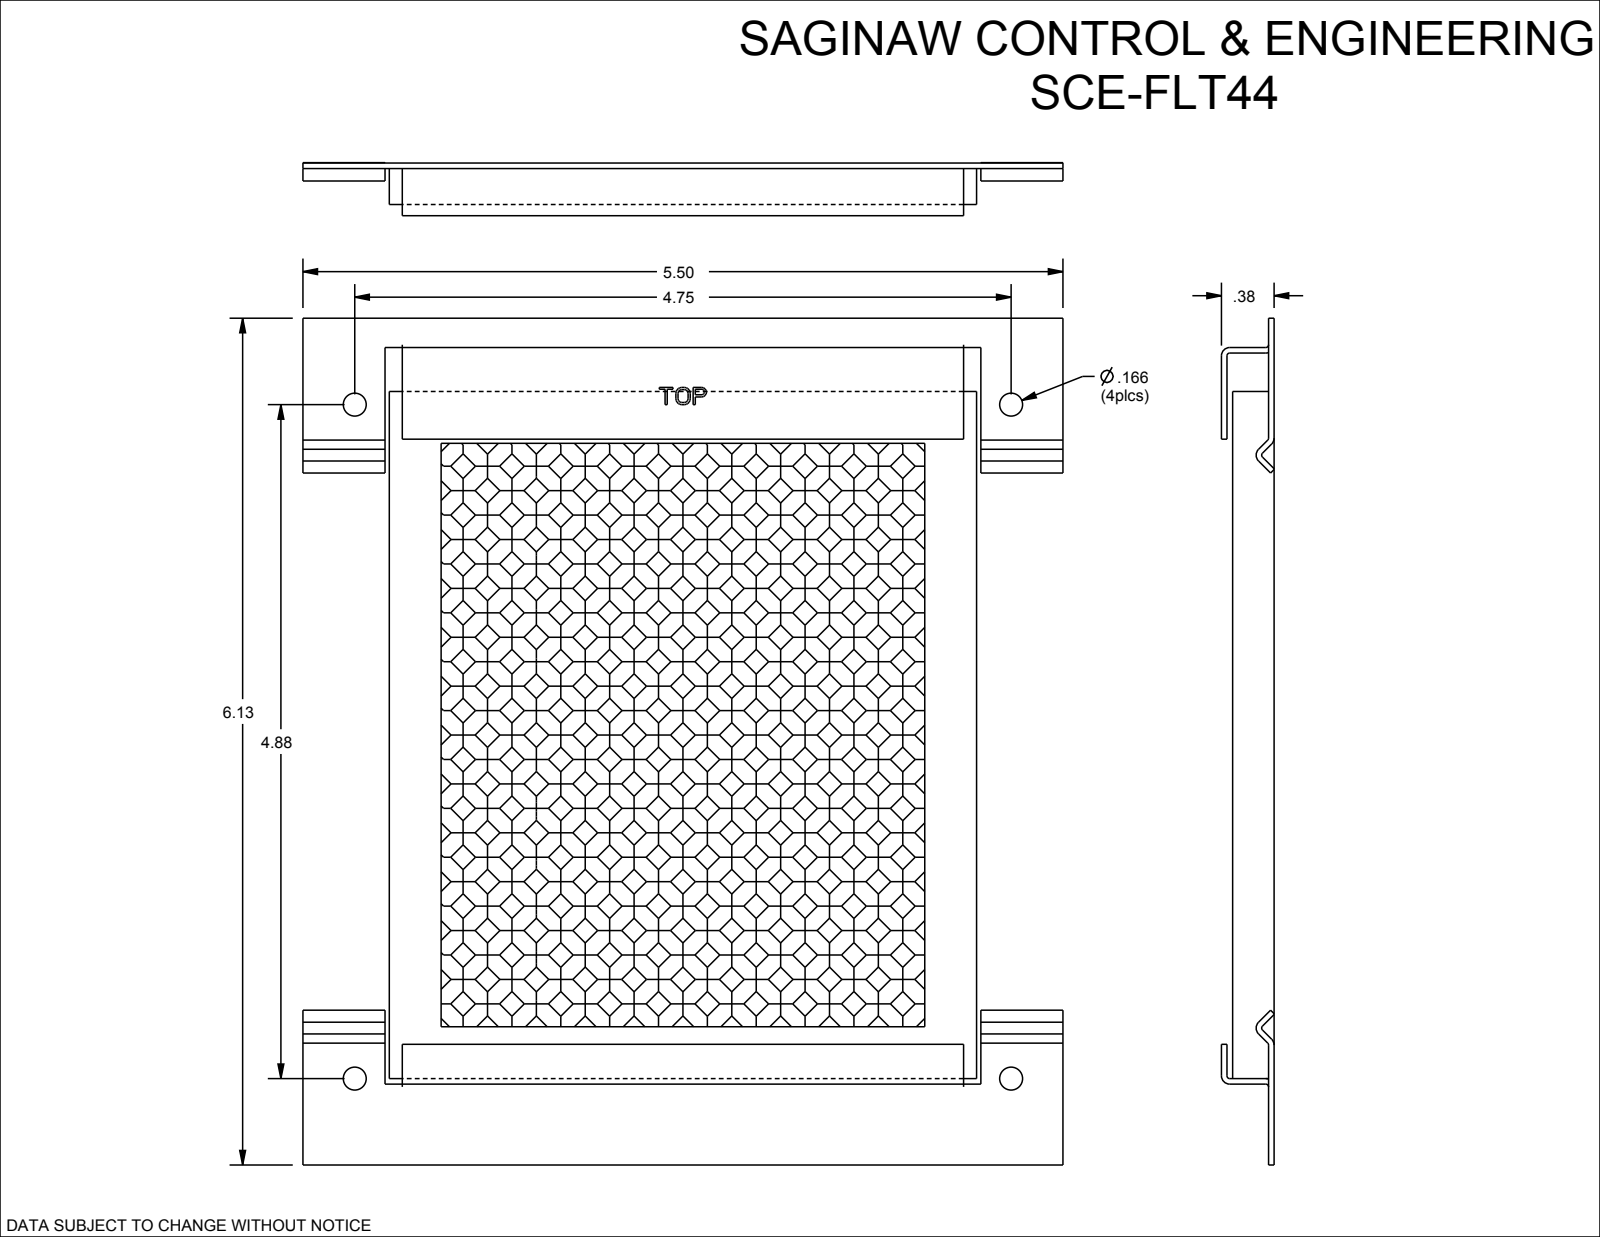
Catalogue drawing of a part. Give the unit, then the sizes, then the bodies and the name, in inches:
Units: inches
Overall size (bounding box): 6.125 × 5.5 × 0.384
Round holes (diameter × count): ⌀0.166 ×4
Round bosses / shafts (diameter × count): ⌀0.125 ×29, ⌀0.125 ×15
Partial cylindrical surfaces — rounded edges, fillets, slot ends (radius × count): R0.02 ×8, R0.06 ×8
Main face-to-face distances: 0.04, 0.3, 0.26, 0.14, 0.12, 0.16, 0.16, 0.02, 0.1, 0.14
Hole centre spacings: 4.75, 4.875, 6.806
Volume: 3.627 in³ · Surface area: 85.08 in²
Bodies: 3 solids, 1626 faces (638 planar, 988 cylindrical, 0 other)
Part name (STEP PRODUCT): SCE-FLT44
STEP written by: SolidWorks 2019 (CONFIG_CONTROL_DESIGN)
